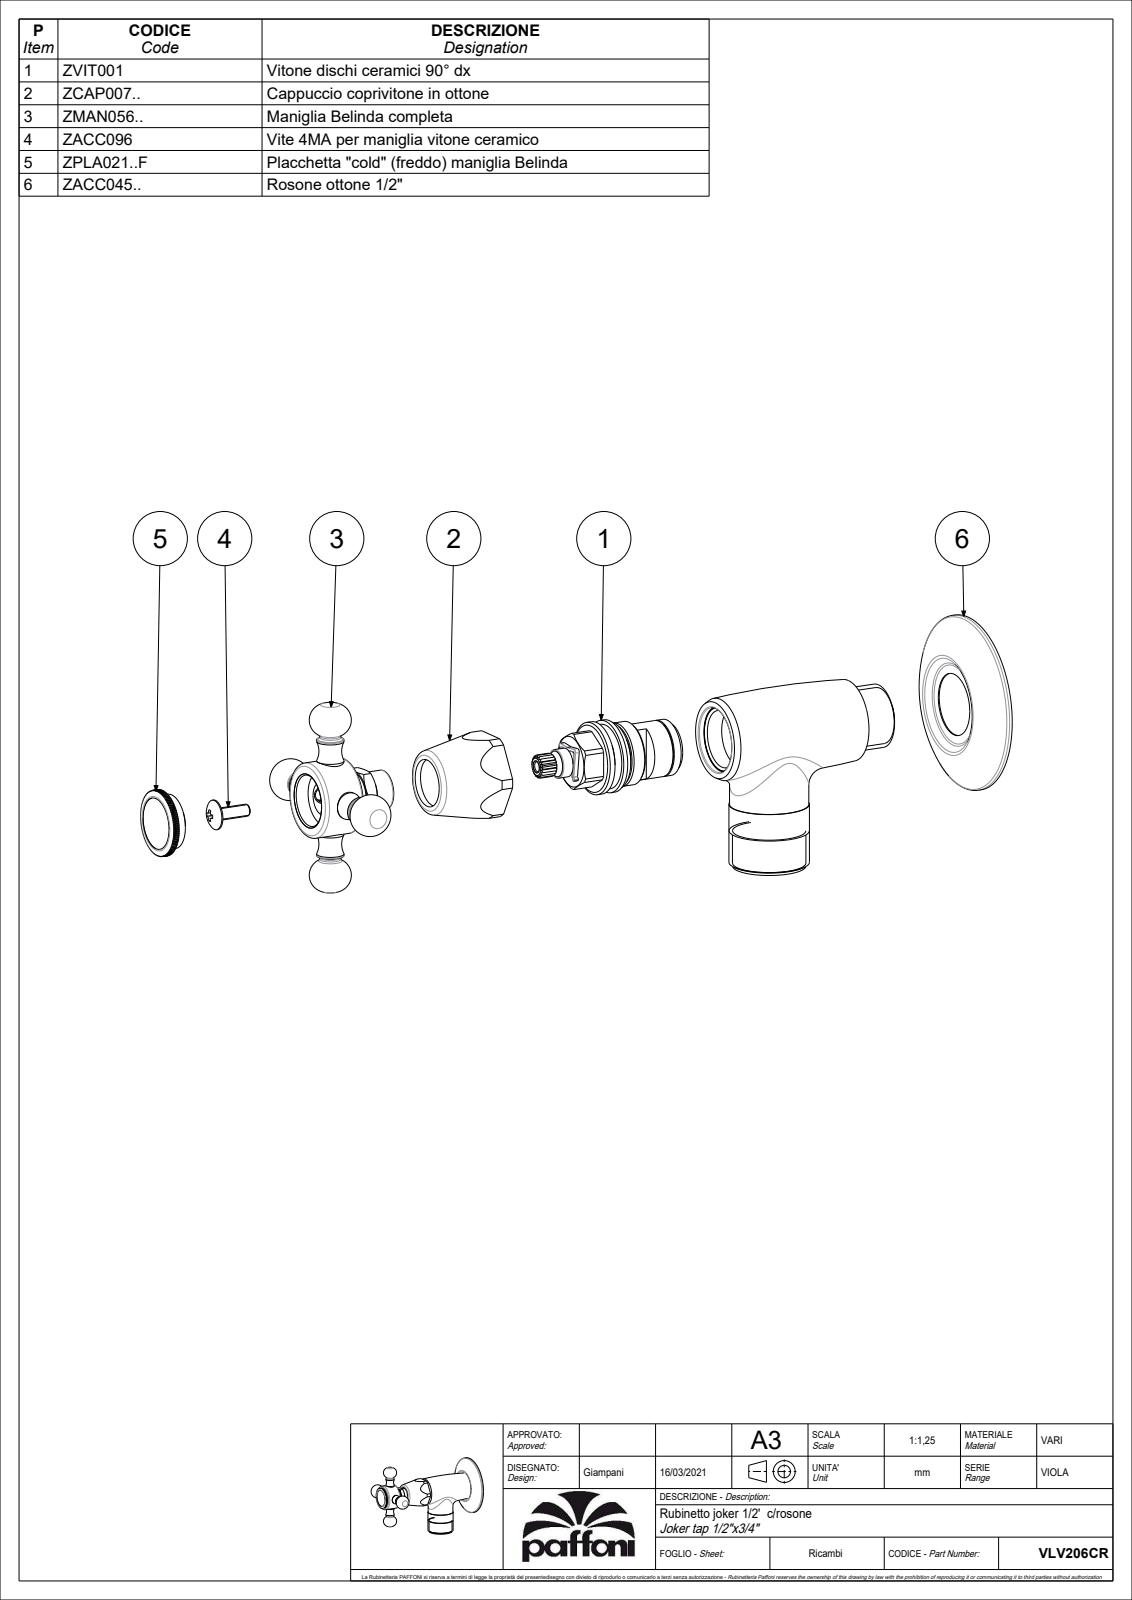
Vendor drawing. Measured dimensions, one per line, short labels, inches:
name: VLV206CR
written by: CREO PARAMETRIC BY PTC INC, 2020044 (CONFIG_CONTROL_DESIGN)
unit: in
bodies: 1 solid, 468 faces (228 planar, 148 cylindrical, 92 other)
size: 4.504 × 3.053 × 2.522
volume: 5.713 in³; area: 31.91 in²
bosses: 2× ⌀0.354, 2× ⌀0.276, 1× ⌀2.283, 1× ⌀1.039, 1× ⌀1.024, 1× ⌀0.984, 1× ⌀0.945, 1× ⌀0.827
rounds: 1× R0.433, 1× R0.571
face distances: 3.583, 1.043, 0.264, 3.846, 0.817, 0.226, 3.406, 3.142, 0.441, 1.27
